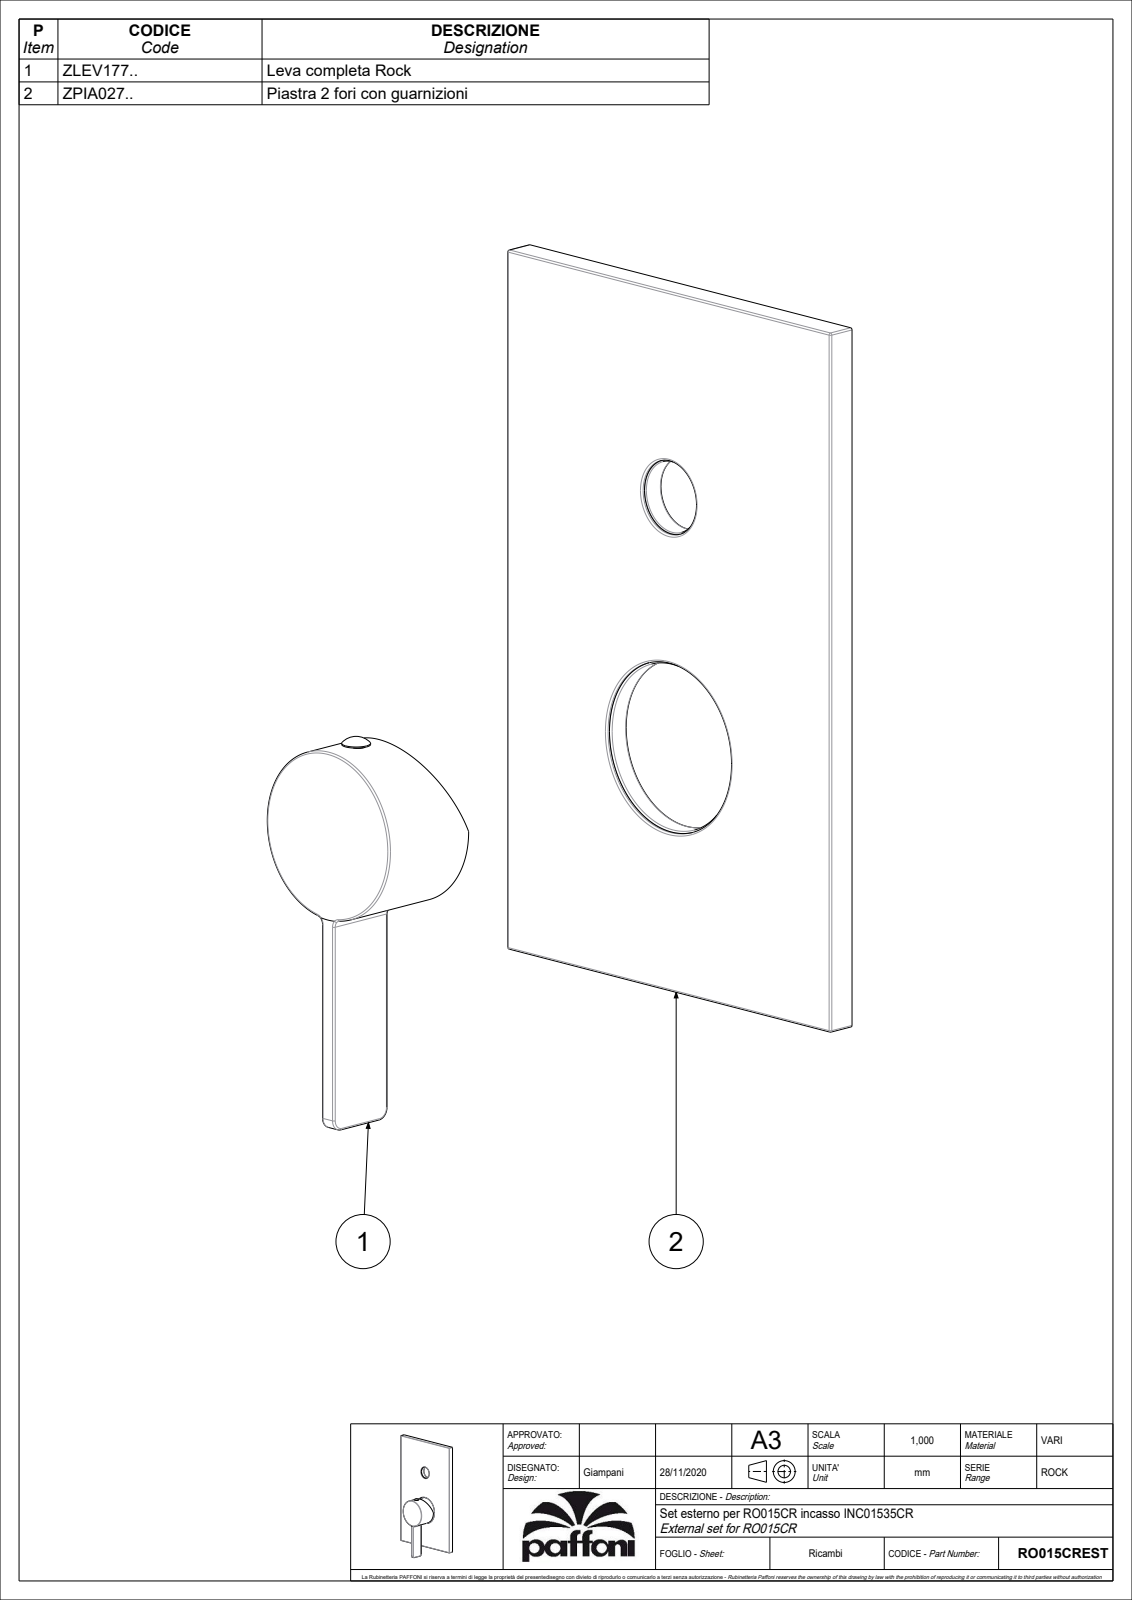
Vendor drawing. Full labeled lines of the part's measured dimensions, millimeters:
Part name (STEP PRODUCT): RO015CREST
STEP written by: CREO PARAMETRIC BY PTC INC, 2020044 (CONFIG_CONTROL_DESIGN)
Units: millimetres
Bodies: 2 solids, 209 faces (70 planar, 69 cylindrical, 70 other)
Overall size (bounding box): 204 × 120 × 40
Volume: 133 331 mm³ · Surface area: 68 746 mm²
Round holes (diameter × count): ⌀3 ×1, ⌀19.2 ×1, ⌀20 ×1, ⌀23.2 ×1, ⌀45 ×1, ⌀46 ×1
Round bosses / shafts (diameter × count): ⌀51 ×1, ⌀49 ×1, ⌀45.5 ×1, ⌀25 ×1, ⌀23 ×1, ⌀7.6 ×1, ⌀5.5 ×1, ⌀5 ×1
Partial cylindrical surfaces — rounded edges, fillets, slot ends (radius × count): R0.5 ×17, R1 ×8, R0.3 ×2, R1.5 ×2, R2 ×2, R3 ×2, R3.5 ×1
Main face-to-face distances: 7.5, 2.5, 5, 0.5, 22.5, 57.75, 62.25, 4.5, 8, 97.5
Hole centre spacings: 68
